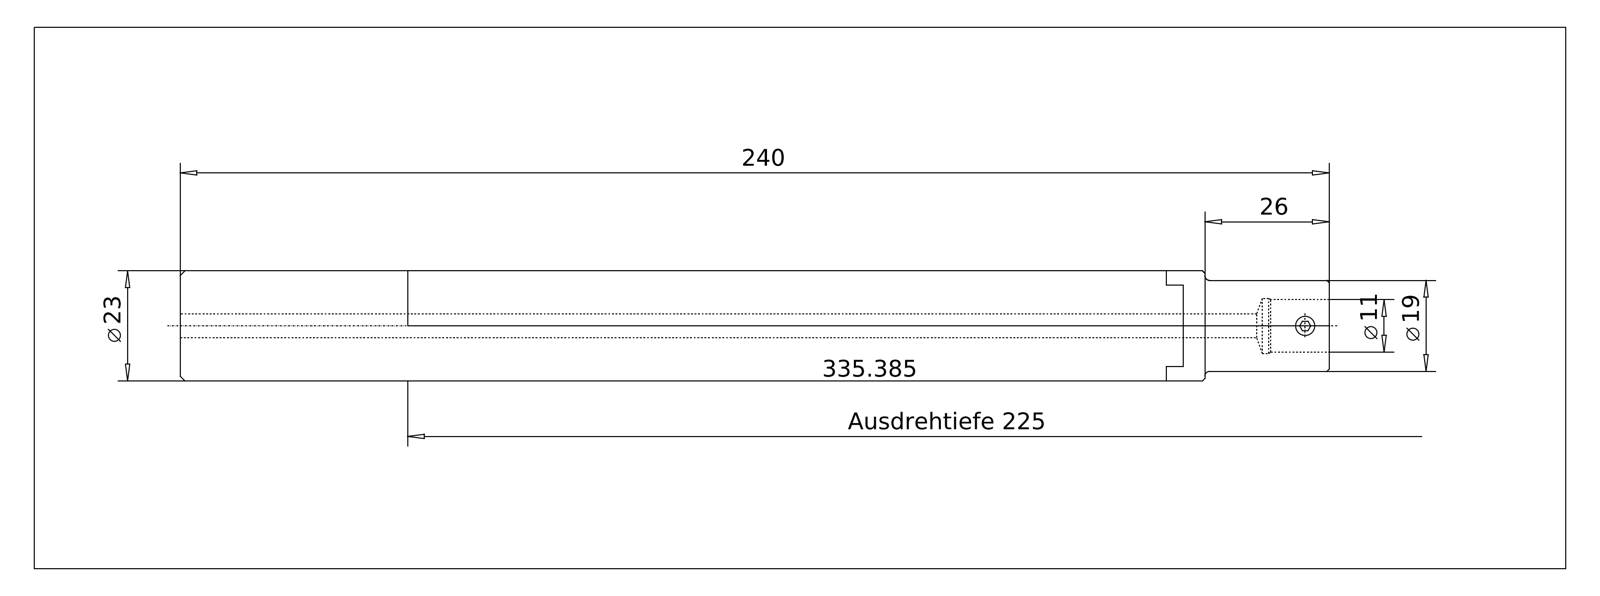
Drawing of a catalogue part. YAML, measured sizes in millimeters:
part_name: "335.385 Kaiser D23 X CK1 X 205HM|335.385 Kaiser D23 X CK1 X 205HM;NONE; 335.385 Kaiser D23 X CK1 X 205HM|690.431 Kaiser ETL M4 X 5 CK1;NONE"
step_written_by: "ACIS (automotive_design)"
units: millimeters
bodies: {solids: 2, faces: 70, planar: 27, cylindrical: 18, other: 25}
overall_size: [240, 23, 23]
volume: 90370
surface_area: 21916
round_holes:
  - {diameter: 3.2, count: 1}
  - {diameter: 4.2, count: 1}
  - {diameter: 5, count: 1}
  - {diameter: 11, count: 1}
  - {diameter: 11.5, count: 1}
round_bosses_or_shafts:
  - {diameter: 23, count: 1}
  - {diameter: 19, count: 1}
  - {diameter: 4, count: 1}
partial_cylinders:
  - {radius: 1.5, count: 2}
face_to_face_distances: [240, 26, 214, 9.34, 5.9, 20.1, 234.1, 5, 1.99, 4.05]
